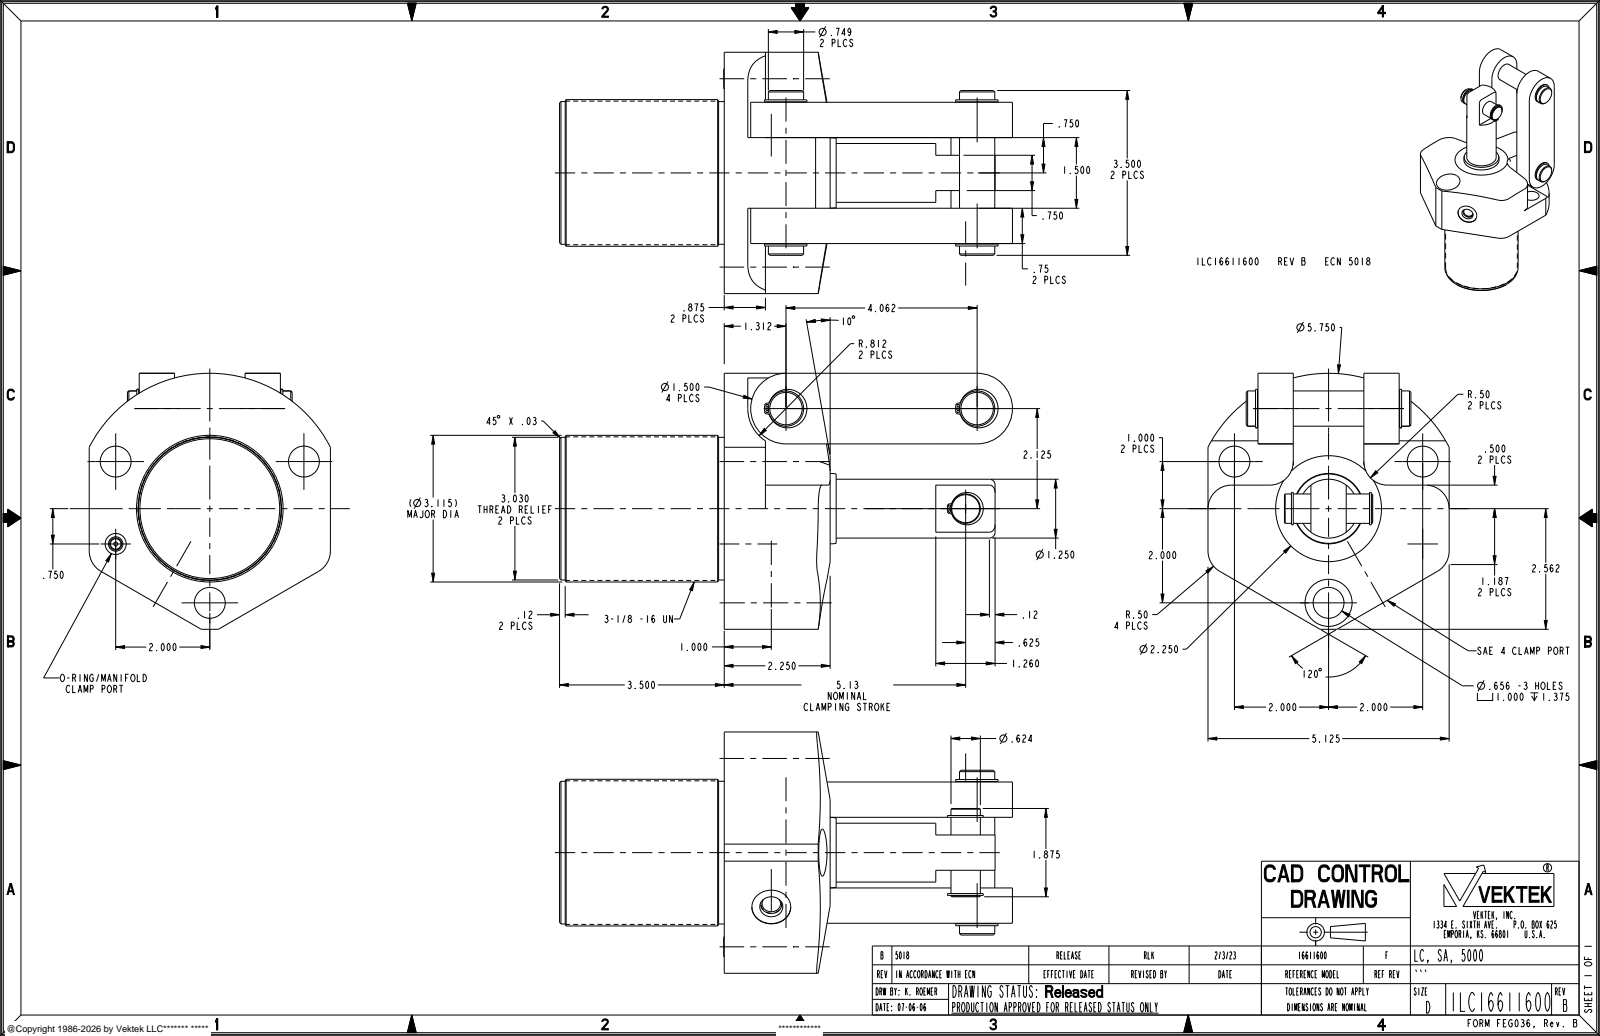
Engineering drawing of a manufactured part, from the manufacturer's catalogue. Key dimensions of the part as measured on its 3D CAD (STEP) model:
Part name (STEP PRODUCT): ILC16611600
STEP written by: CREO PARAMETRIC BY PTC INC, 2021164 (AUTOMOTIVE_DESIGN)
Units: inches
Bodies: 2 solids, 262 faces (107 planar, 119 cylindrical, 36 other)
Overall size (bounding box): 9.624 × 5.438 × 5.125
Volume: 80.51 in³ · Surface area: 235.4 in²
Round holes (diameter × count): ⌀0.052 ×4, ⌀0.656 ×3, ⌀0.047 ×2, ⌀0.753 ×2, ⌀0.098 ×1, ⌀0.256 ×1, ⌀0.392 ×1, ⌀0.447 ×1, ⌀0.825 ×1, ⌀1 ×1
Round bosses / shafts (diameter × count): ⌀0.819 ×2, ⌀0.749 ×2, ⌀3.115 ×1, ⌀3.049 ×1, ⌀3.03 ×1, ⌀1.25 ×1, ⌀0.688 ×1, ⌀0.624 ×1
Partial cylindrical surfaces — rounded edges, fillets, slot ends (radius × count): R0.052 ×8, R0.5 ×6, R0.047 ×4, R0.75 ×2, R0.812 ×1, R2.875 ×1
Main face-to-face distances: 2.25, 0.75, 3.5, 3, 1.5, 1.5, 1.063, 1.813, 3.313, 4.063
Hole centre spacings: 0.125, 0.408, 0.409, 3.606, 3.659, 4.062, 4.064, 4.466
